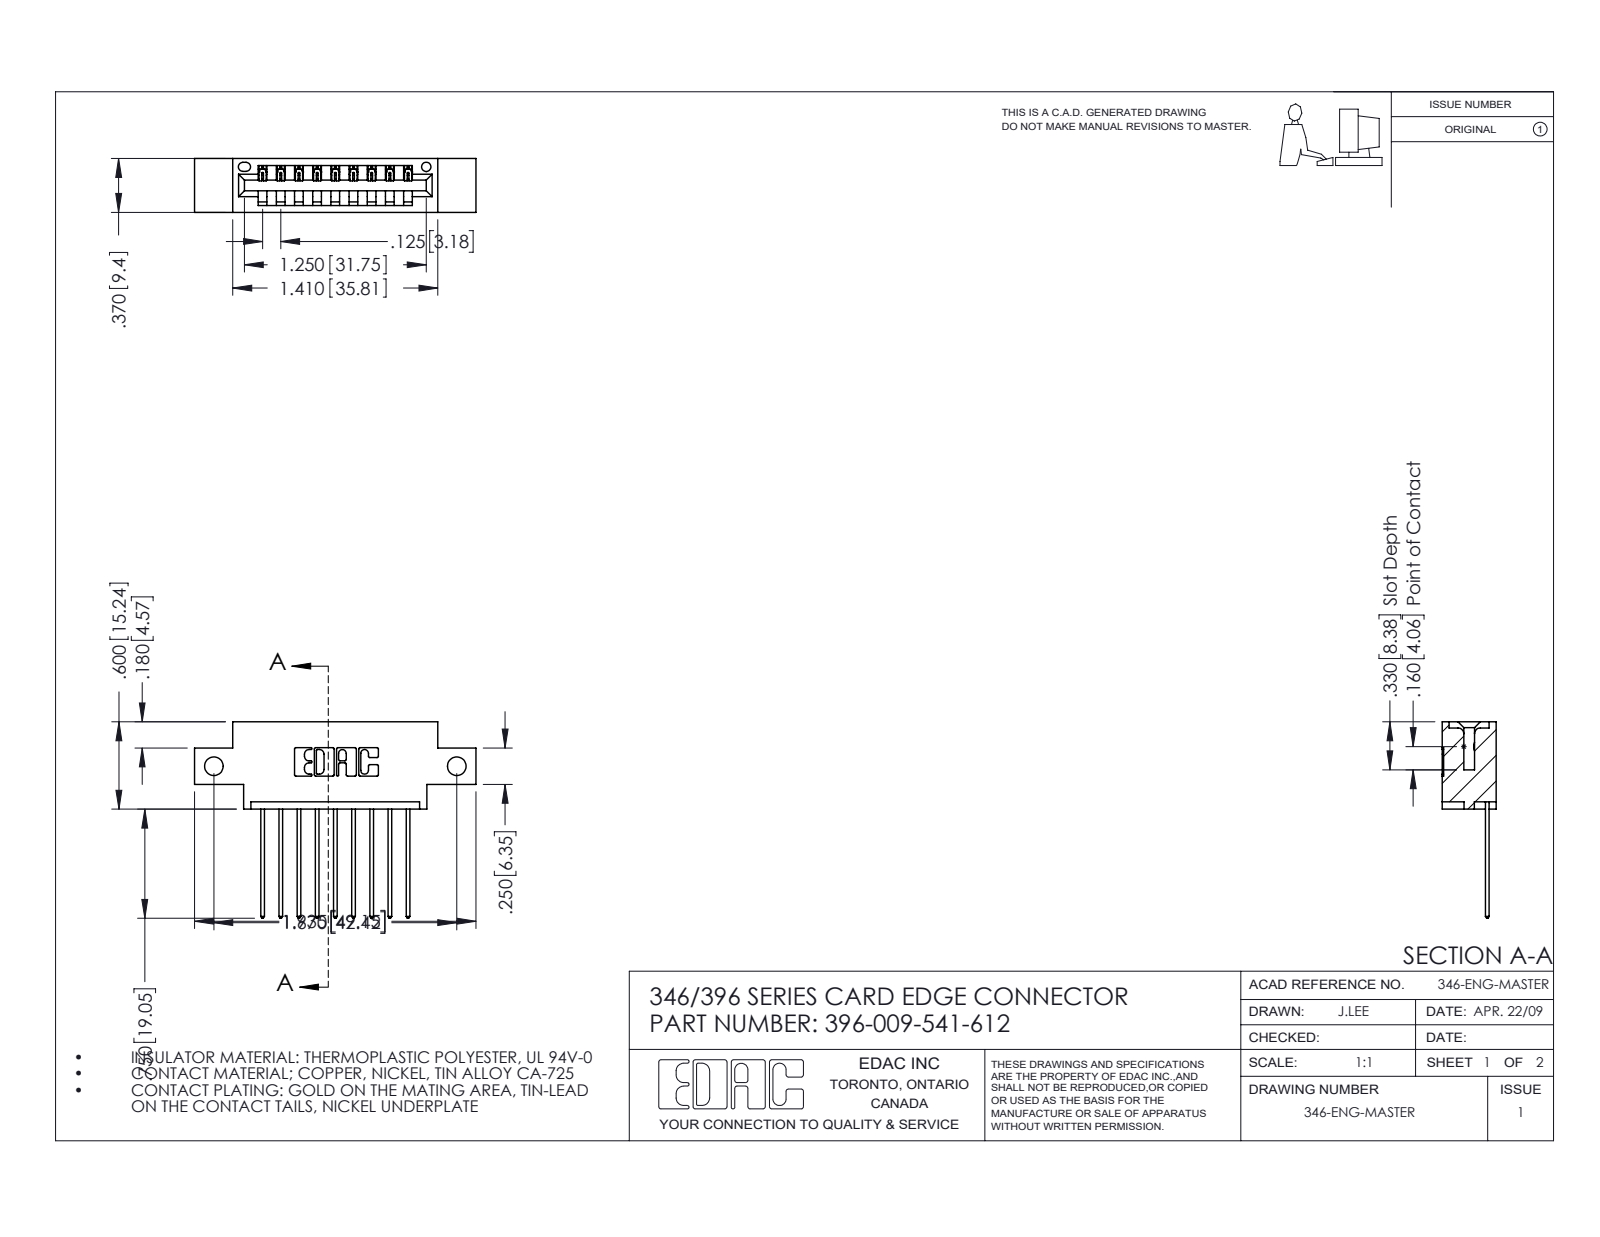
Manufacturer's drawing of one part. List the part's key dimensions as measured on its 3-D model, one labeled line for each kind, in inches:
Part name (STEP PRODUCT): 346 Part_0.170 Offset - Side Mount; 396-009-541-612; 345-292-001_345-293-141
STEP written by: SolidWorks 2016 (CONFIG_CONTROL_DESIGN)
Units: inches
Bodies: 10 solids, 648 faces (440 planar, 208 cylindrical, 0 other)
Overall size (bounding box): 1.935 × 1.35 × 0.37
Volume: 0.26 in³ · Surface area: 8.008 in²
Round holes (diameter × count): ⌀0.128 ×2, ⌀0.064 ×1
Partial cylindrical surfaces — rounded edges, fillets, slot ends (radius × count): R0.01 ×22, R0.006 ×18, R0.01 ×18, R0.007 ×6, R0.031 ×6, R0.026 ×3, R0.031 ×2, R0.04 ×2
Main face-to-face distances: 0.25, 0.37, 0.048, 0.322, 0.072, 0.298, 0.025, 0.148, 0.222, 0.1
Hole centre spacings: 1.67
